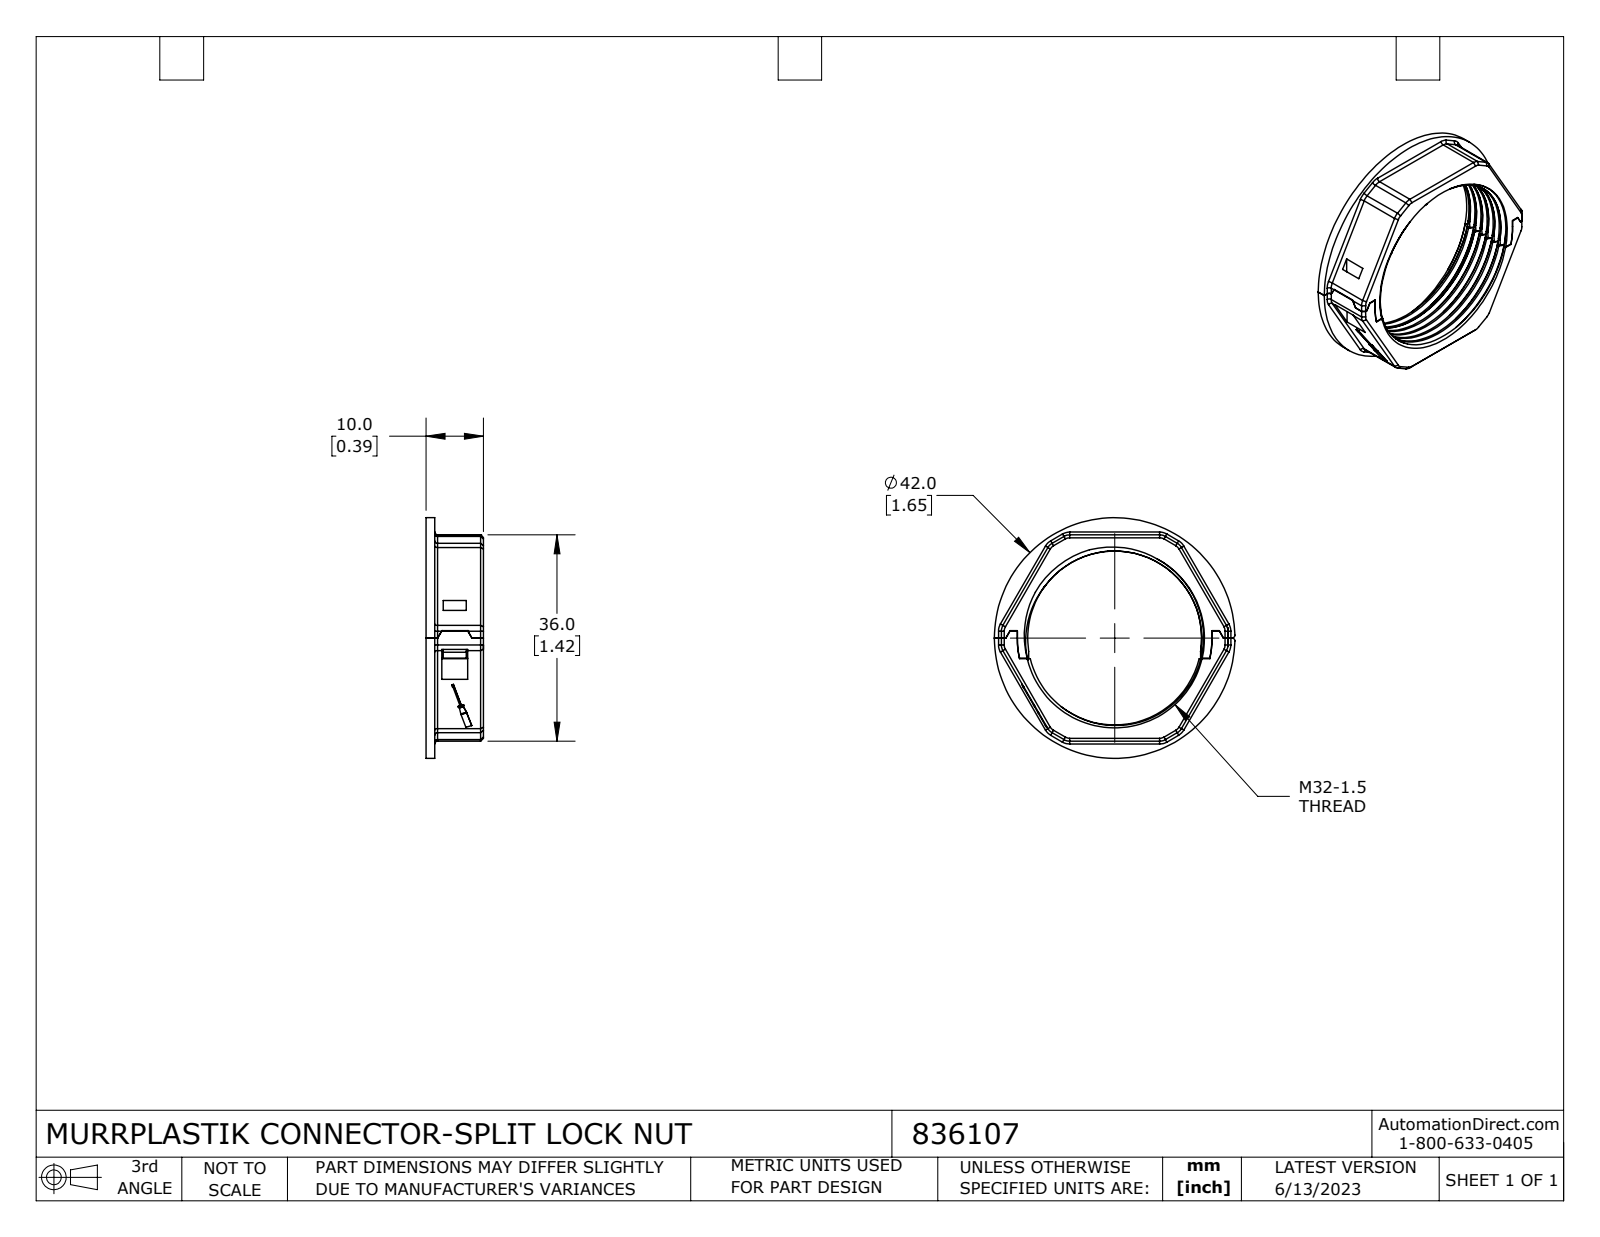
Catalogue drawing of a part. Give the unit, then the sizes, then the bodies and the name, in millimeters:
Units: millimetres
Overall size (bounding box): 42 × 42 × 10
Round holes (diameter × count): ⌀6 ×1, ⌀30.4 ×1, ⌀32 ×1
Round bosses / shafts (diameter × count): ⌀42 ×1
Partial cylindrical surfaces — rounded edges, fillets, slot ends (radius × count): R0.5 ×14, R2 ×12, R0.1 ×2, R17 ×1
Main face-to-face distances: 36, 10, 1.5, 8.5, 34, 18, 4.8, 2, 16, 19.2
Volume: 3 800 mm³ · Surface area: 4 466 mm²
Bodies: 2 solids, 453 faces (224 planar, 85 cylindrical, 144 other)
Part name (STEP PRODUCT): 836107
STEP written by: SolidWorks 2021 (CONFIG_CONTROL_DESIGN)
